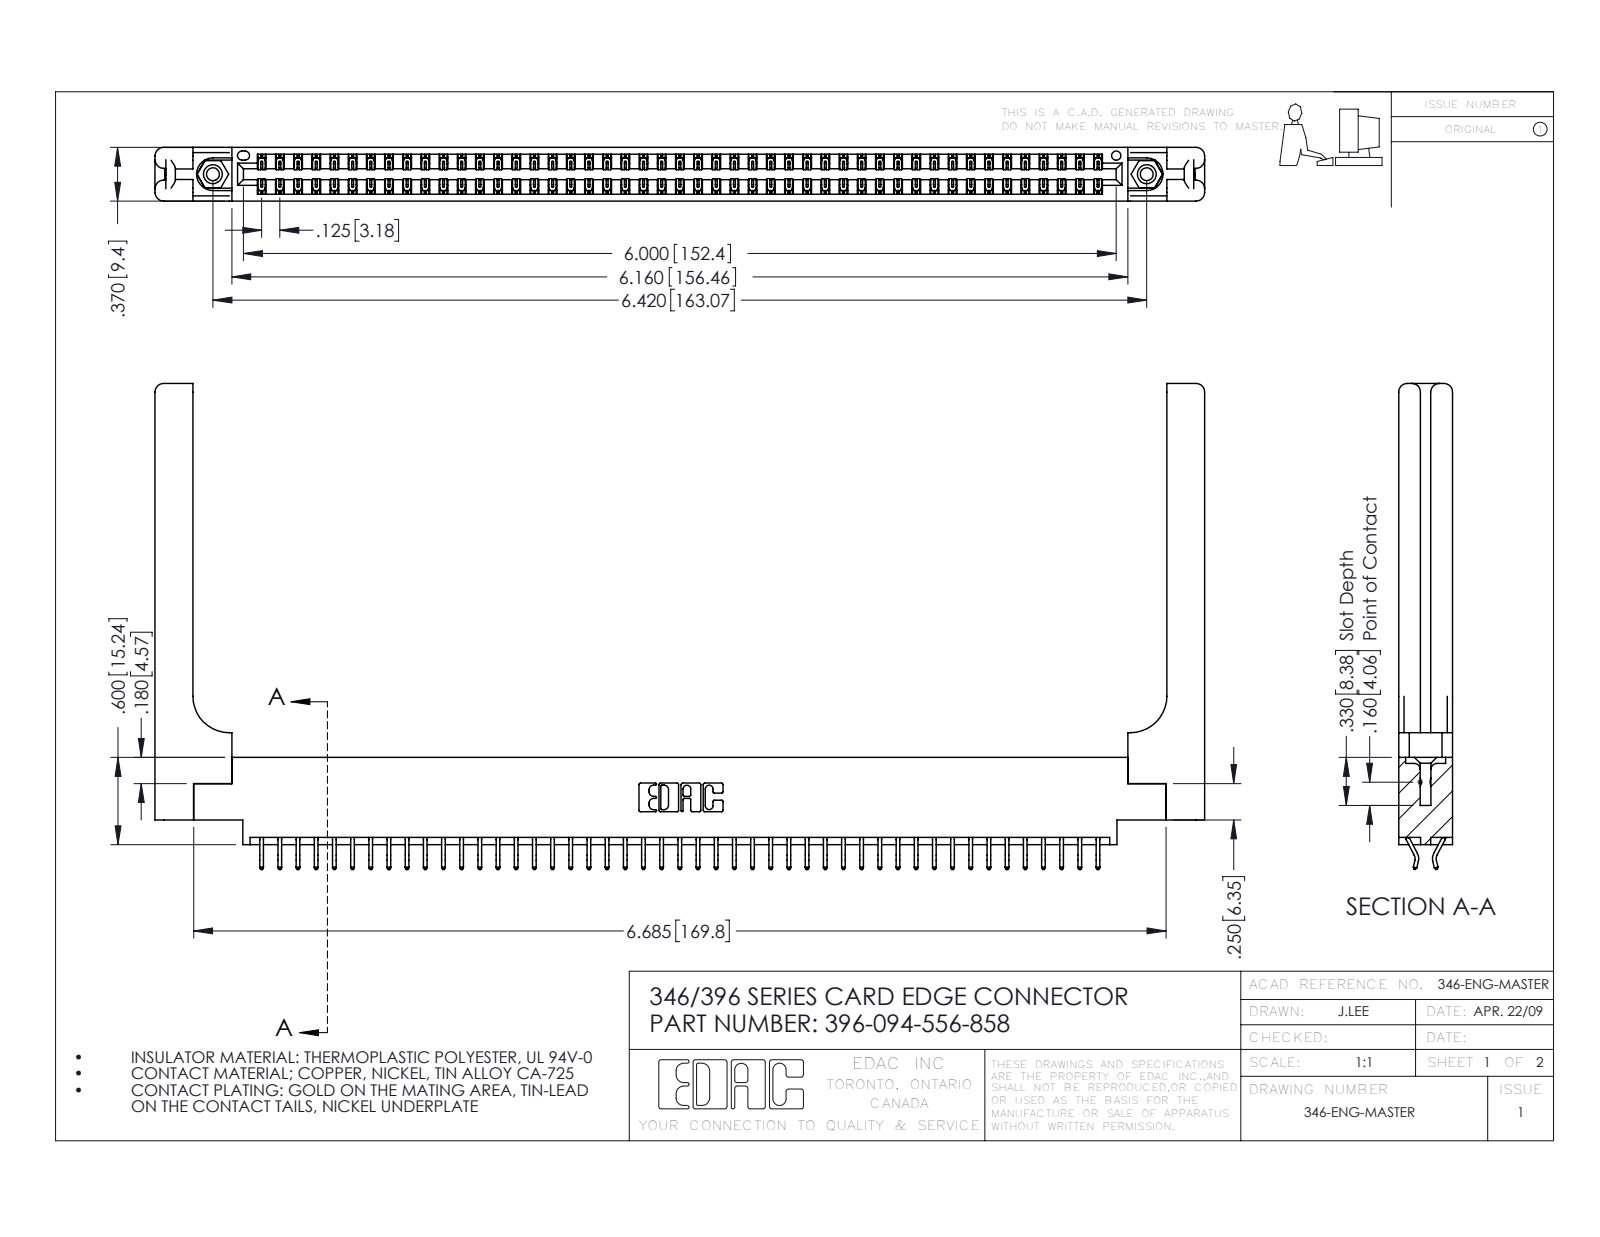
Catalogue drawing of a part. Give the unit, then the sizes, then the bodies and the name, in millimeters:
Units: millimetres
Overall size (bounding box): 183.3 × 84.8 × 9.4
Round holes (diameter × count): ⌀2.3 ×2, ⌀3.2 ×2, ⌀4 ×2, ⌀1.6 ×1
Round bosses / shafts (diameter × count): ⌀3.9 ×2
Partial cylindrical surfaces — rounded edges, fillets, slot ends (radius × count): R0.2 ×141, R0.3 ×22, R1.5 ×16, R0.2 ×6, R0.8 ×6, R0.7 ×3, R0.3 ×2, R0.4 ×2
Main face-to-face distances: 9.4, 1.2, 8.2, 1.8, 3.8, 3.8, 6.4, 0.6, 7.6, 7
Hole centre spacings: 6.2, 157.8, 163.1
Volume: 25 250 mm³ · Surface area: 29 550 mm²
Bodies: 99 solids, 5834 faces (3894 planar, 1880 cylindrical, 60 other)
Part name (STEP PRODUCT): 346-220-058_345-220-058; 345-292-001_556 Tail; 346 Part_0.170 Offset - 0.156 Dia-TH; 345-250-001_345-250-001-102 (+1 more)
STEP written by: SolidWorks 2016 (CONFIG_CONTROL_DESIGN)
